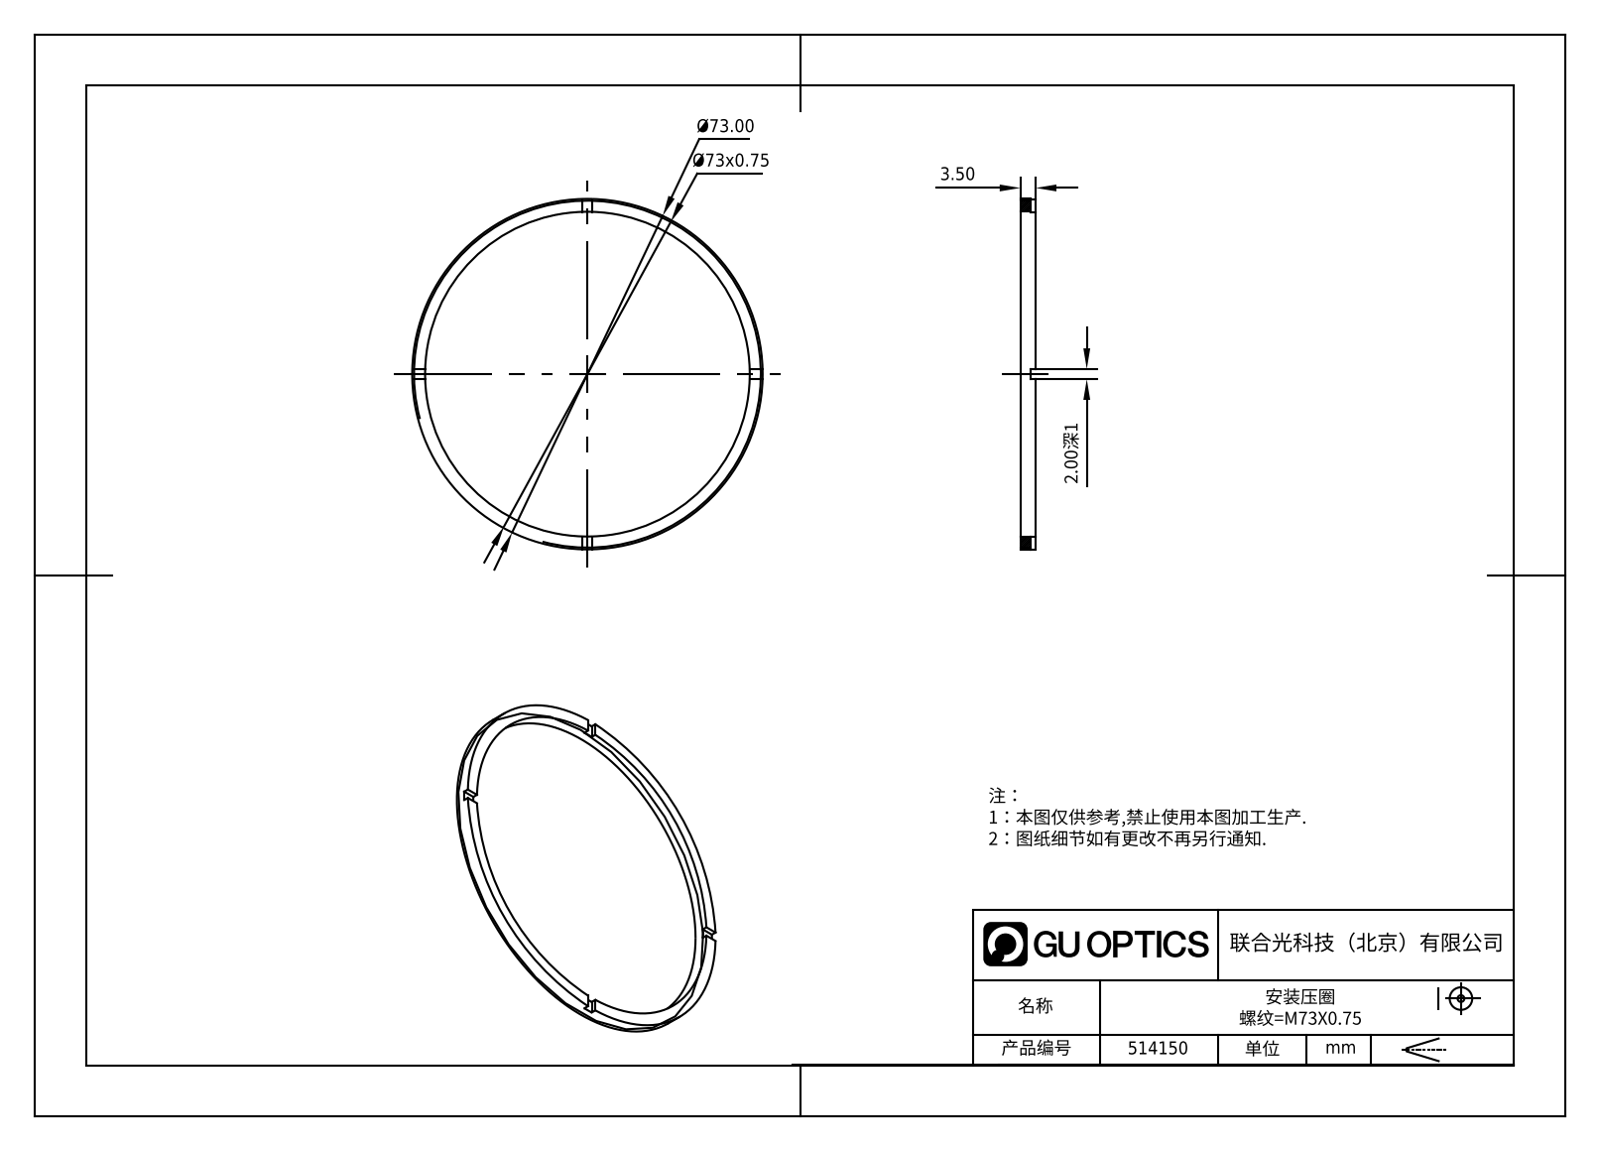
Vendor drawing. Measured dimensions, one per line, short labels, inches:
name: 514150
written by: SolidWorks 2020 (CONFIG_CONTROL_DESIGN)
unit: in
bodies: 1 solid, 21 faces (17 planar, 4 cylindrical, 0 other)
size: 2.874 × 2.874 × 0.138
volume: 0.139 in³; area: 4.444 in²
holes: 1× ⌀2.638
bosses: 1× ⌀2.874
face distances: 0.138, 0.098, 0.039, 0.079
